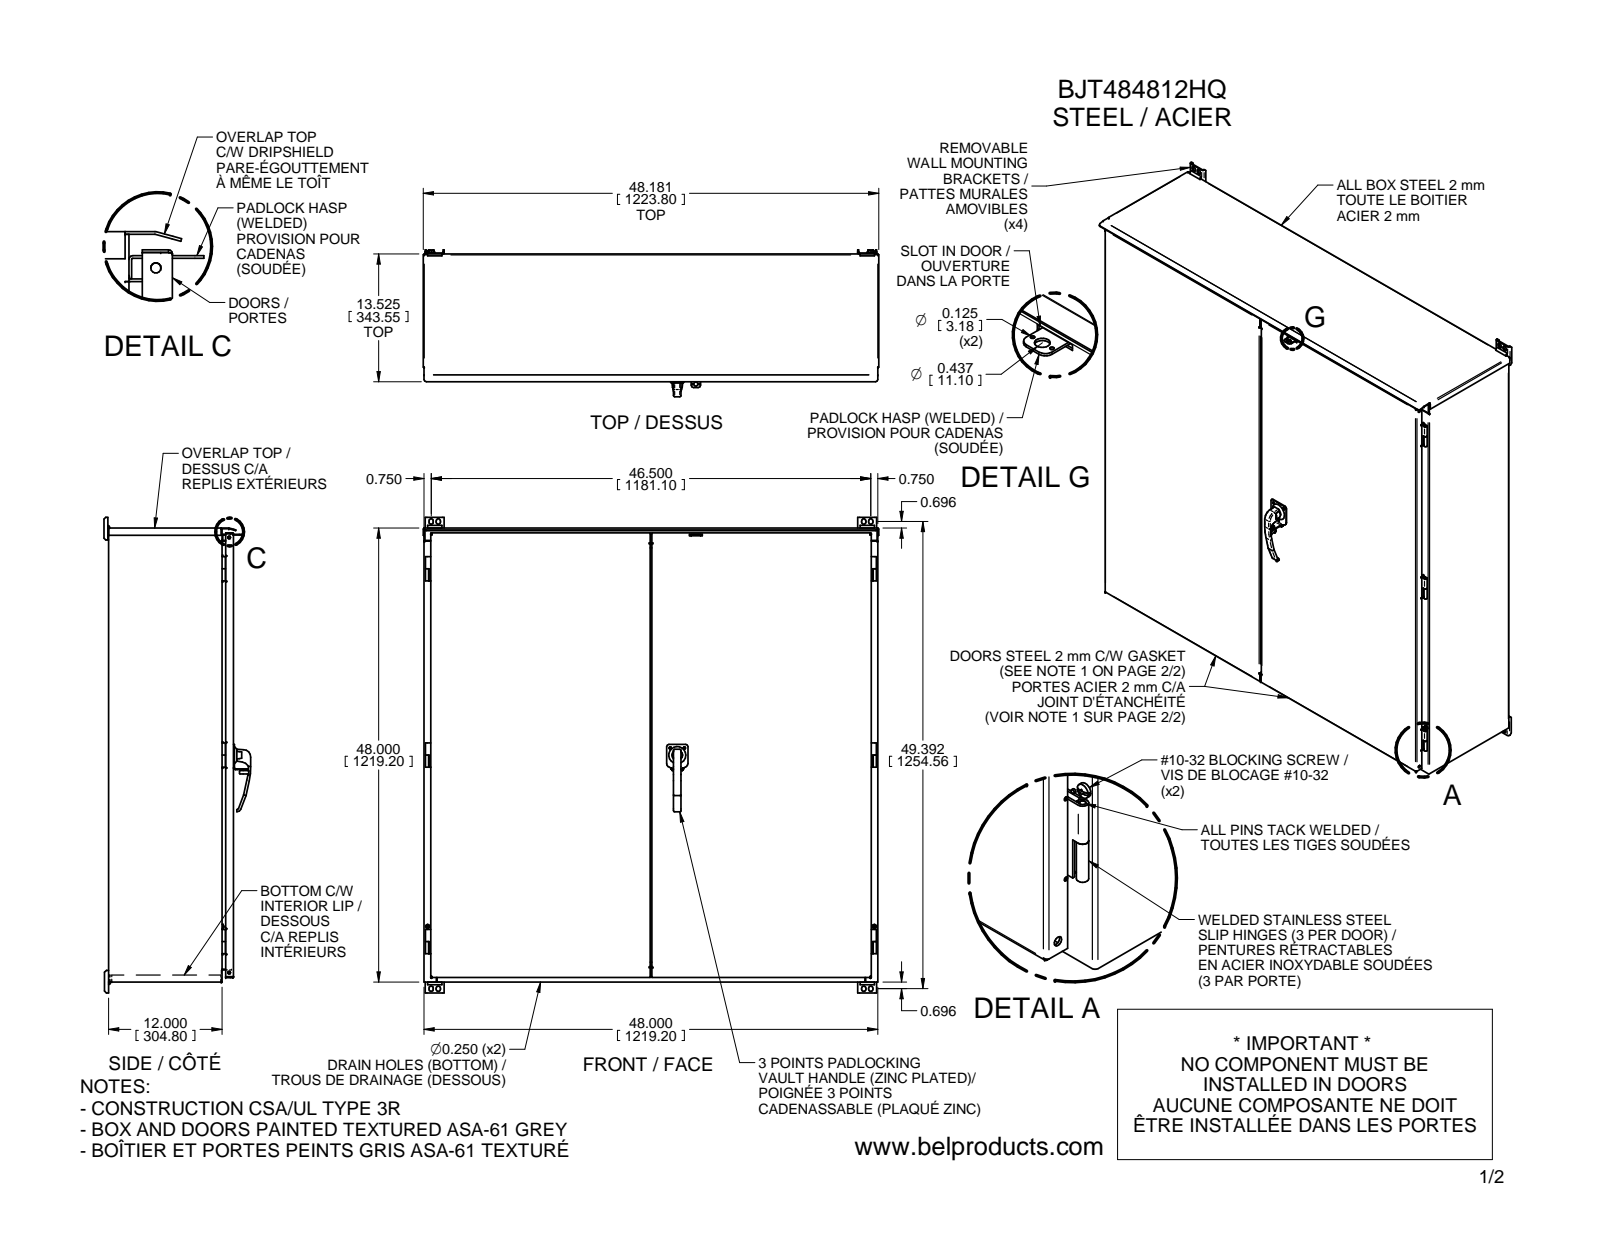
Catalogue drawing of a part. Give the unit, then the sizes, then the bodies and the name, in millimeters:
Units: millimetres
Overall size (bounding box): 1276.76 × 1223.8 × 394.67
Round holes (diameter × count): ⌀3.16 ×24, ⌀3.17 ×18, ⌀7.92 ×10, ⌀11.58 ×8, ⌀5.11 ×7, ⌀12.7 ×6, ⌀7.14 ×4, ⌀9.02 ×4, ⌀9.53 ×4, ⌀10.31 ×4, ⌀10.54 ×4, ⌀6.38 ×3
Round bosses / shafts (diameter × count): ⌀3.17 ×24, ⌀3.02 ×16, ⌀20.62 ×4, ⌀25.12 ×2, ⌀10.87 ×2, ⌀8.56 ×2, ⌀7.8 ×2, ⌀6.35 ×2
Partial cylindrical surfaces — rounded edges, fillets, slot ends (radius × count): R0.81 ×46, R2.72 ×38, R5.79 ×16, R1.59 ×15, R3.17 ×12, R2.1 ×8, R2.34 ×8, R4.76 ×8
Main face-to-face distances: 1.91, 333.32, 331.41, 1.9, 335.23, 1217.3, 1219.2, 1215.39, 1215.4, 1217.29
Hole centre spacings: 500.66, 68.66, 432, 533.4, 535.81, 670.58, 1279.9, 50.8
Volume: 10 630 000 mm³ · Surface area: 10 870 000 mm²
Bodies: 60 solids, 1379 faces (860 planar, 403 cylindrical, 116 other)
Part name (STEP PRODUCT): BJT484812HQ-A8F3; BJT484812HQ_BOITIER; BJT484812HQ-B; BJT484812HQ-EB (+8 more)
STEP written by: ST-DEVELOPER v16.7 (AUTOMOTIVE_DESIGN)
